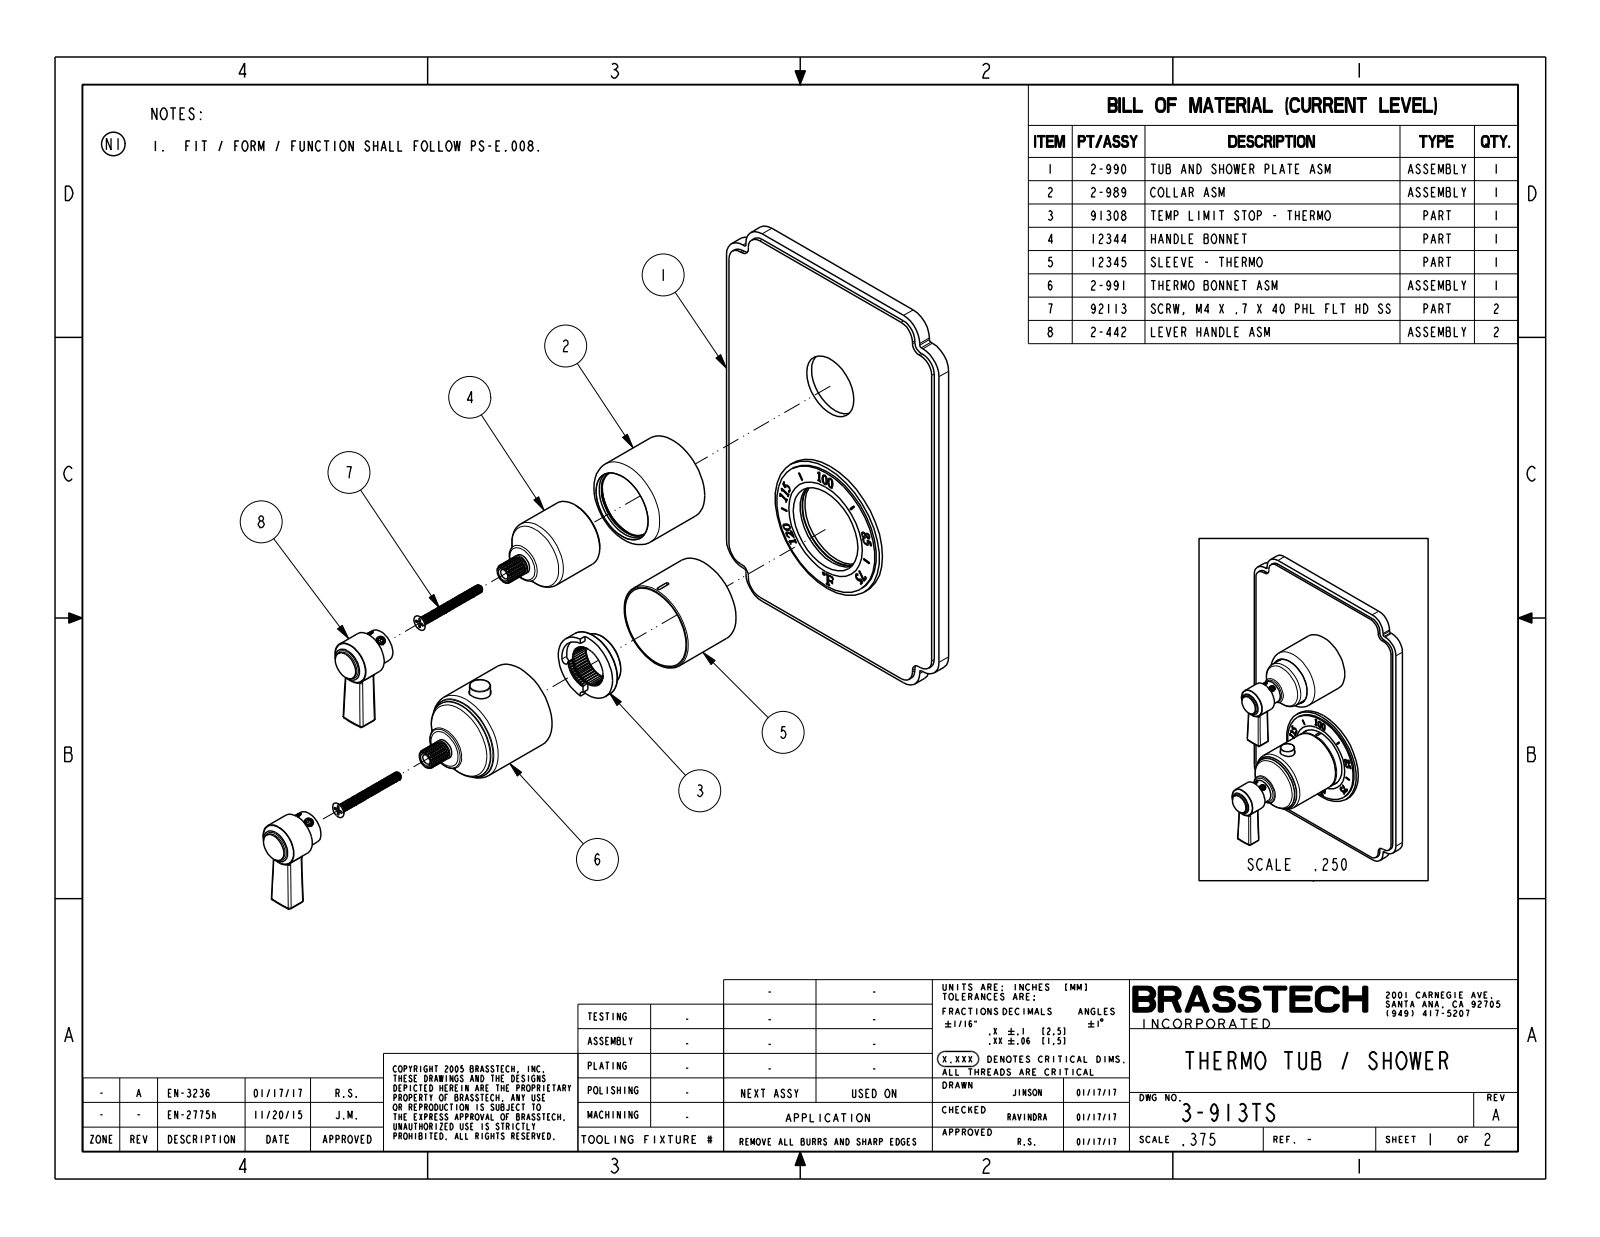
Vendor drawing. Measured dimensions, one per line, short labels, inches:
name: 12343_AF2; H-78_2_FEET_AF4; 91678; 2-990_AF2_ASM (+8 more)
written by: PRO/ENGINEER BY PARAMETRIC TECHNOLOGY CORPORATION, 2013150 (CONFIG_CONTROL_DESIGN)
unit: in
bodies: 20 solids, 2233 faces (909 planar, 487 cylindrical, 837 other)
size: 8.25 × 5.5 × 4.192
volume: 9.642 in³; area: 325.2 in²
holes: 4× ⌀0.136, 2× ⌀0.19, 2× ⌀0.339, 1× ⌀0.063, 1× ⌀0.079, 1× ⌀0.1, 1× ⌀0.126, 1× ⌀0.276, 1× ⌀0.276, 1× ⌀0.406, 1× ⌀1.015, 1× ⌀1.15
bosses: 4× ⌀0.164, 2× ⌀1.654, 2× ⌀0.8, 2× ⌀0.625, 2× ⌀0.525, 2× ⌀0.512, 2× ⌀0.37, 2× ⌀0.303
rounds: 12× R0.04, 8× R0.09, 8× R0.295, 8× R0.34, 8× R0.42, 4× R0.12, 4× R0.165, 4× R0.37
face distances: 0.08, 0.123, 0.043, 0.06, 0.063, 0.25, 0.017, 5.42, 0.19, 0.233
hole spacings: 1.617, 0.554, 2.596, 3.15
